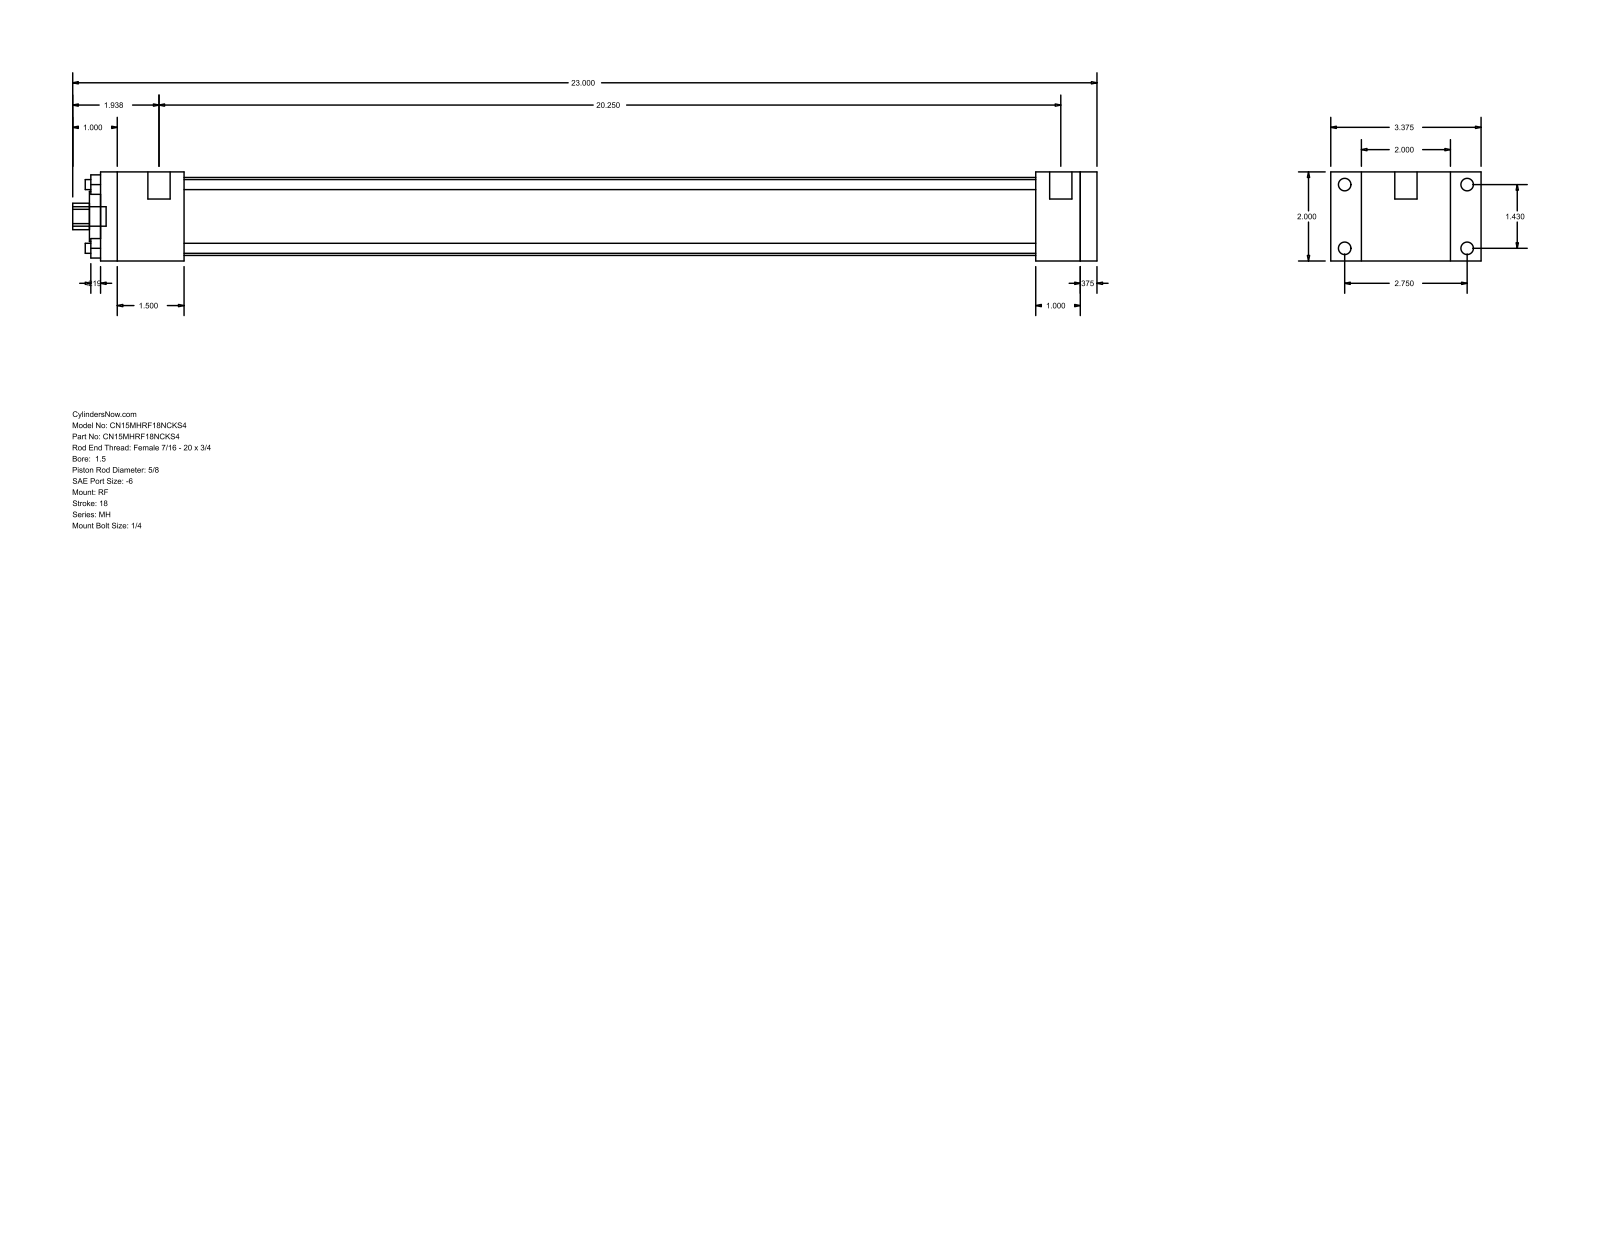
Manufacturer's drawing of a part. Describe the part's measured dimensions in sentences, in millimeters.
The part is named "MH_RF__0150_0.625". Its 3-D file was written by "GSSL Pune (CONFIG_CONTROL_DESIGN)". It is 0 solids with 92 faces: 64 planar, 28 cylindrical and 0 other. Overall it measures 584.2 by 85.72 by 50.8 millimeters. Round holes: 4 of diameter 5.71, 1 of diameter 15.88, 1 of diameter 28.57, 1 of diameter 44.45. Round bosses or shafts: 4 of diameter 7.14, 4 of diameter 5.56, 2 of diameter 12.7, 1 of diameter 11.11. Partial cylindrical surfaces (rounded edges, fillets, slot ends): 1 of radius 7.54. The main face-to-face distances are 50.8, 9.53, 568.32, 558.79, 17.46, 68.26, 533.39, 25.4, 34.93, 47.62. The hole center spacings are 25.68, 36.32, 51.36.
